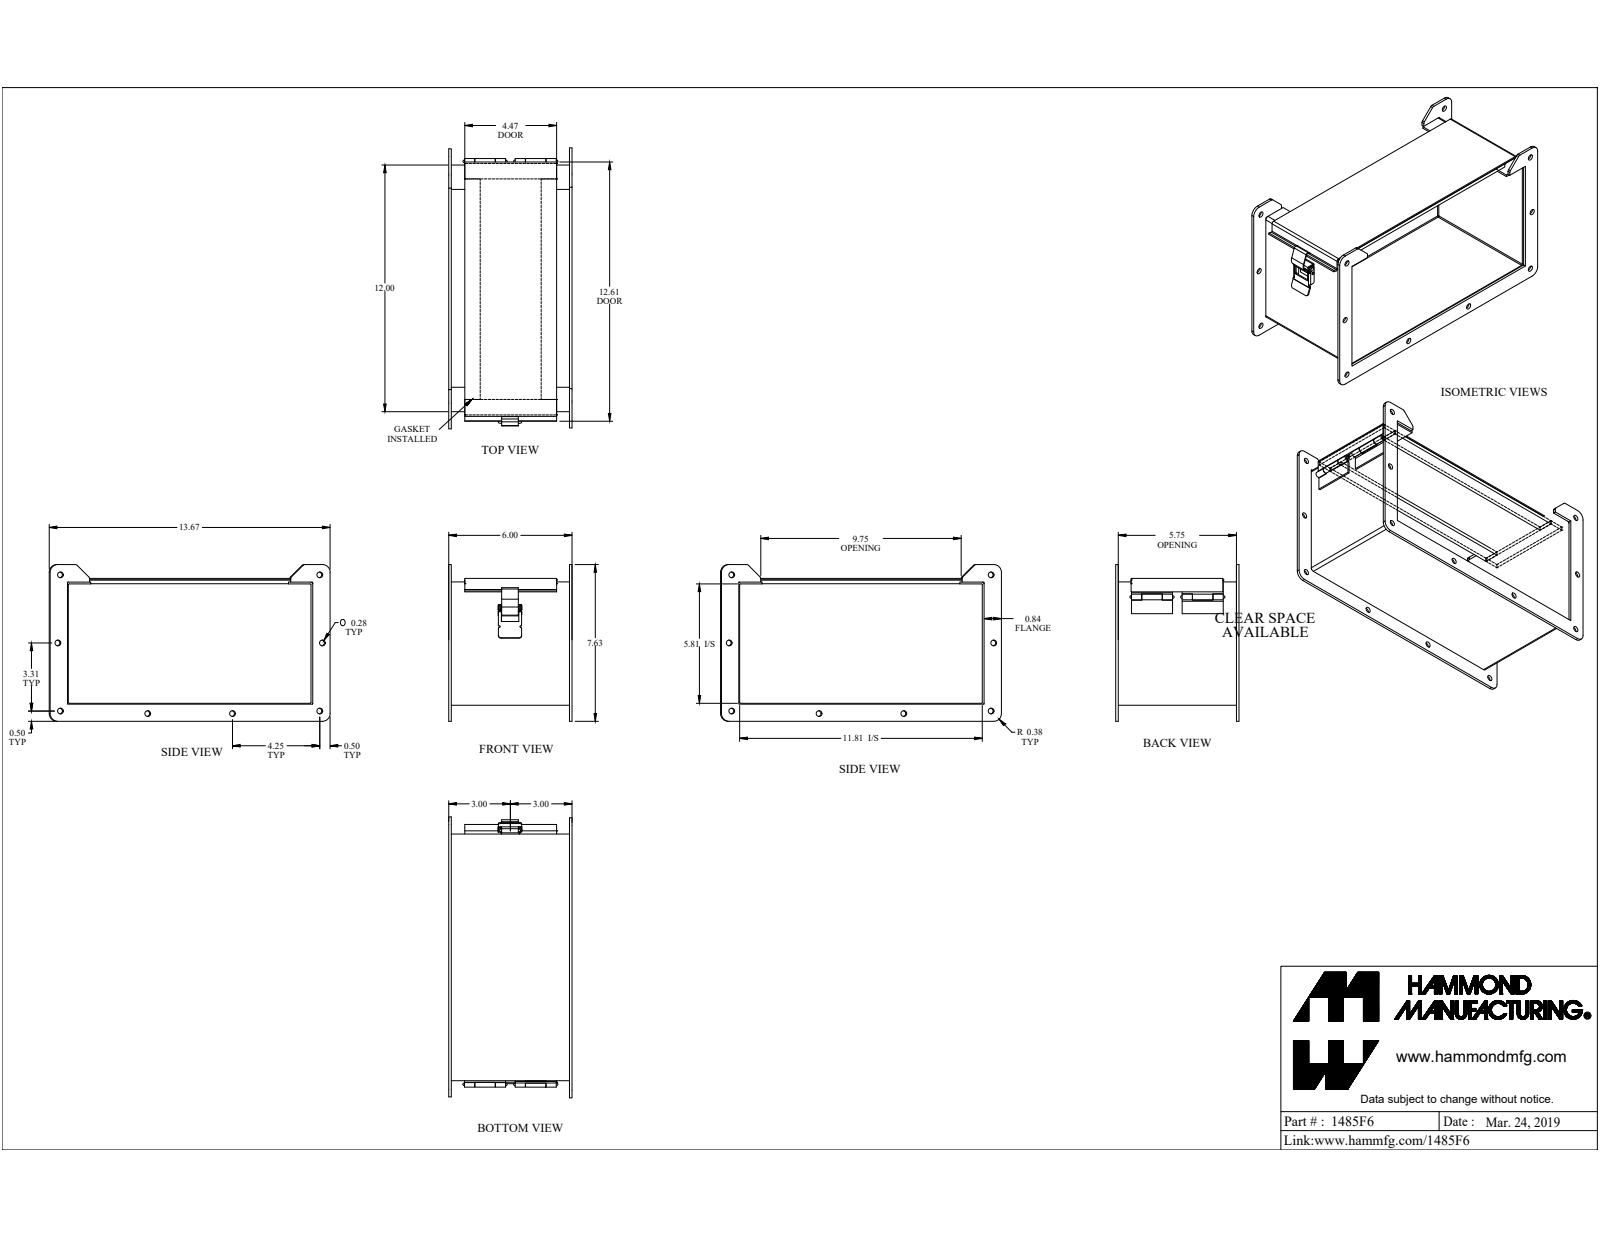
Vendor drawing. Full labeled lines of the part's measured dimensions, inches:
Part name (STEP PRODUCT): 1485F6
STEP written by: SolidWorks 2019 (CONFIG_CONTROL_DESIGN)
Units: inches
Bodies: 17 solids, 304 faces (188 planar, 112 cylindrical, 4 other)
Overall size (bounding box): 13.67 × 7.625 × 6
Volume: 29.58 in³ · Surface area: 627 in²
Round holes (diameter × count): ⌀0.281 ×16, ⌀0.125 ×1, ⌀0.13 ×1, ⌀0.164 ×1
Round bosses / shafts (diameter × count): ⌀0.187 ×2, ⌀0.275 ×1, ⌀0.156 ×1, ⌀0.125 ×1, ⌀0.125 ×1
Partial cylindrical surfaces — rounded edges, fillets, slot ends (radius × count): R0.125 ×11, R0.375 ×8, R0.016 ×7, R0.048 ×4, R0.143 ×4, R0.035 ×3, R0.036 ×3, R0.039 ×3
Main face-to-face distances: 0.095, 6.1, 6.005, 11.905, 0.072, 6.172, 6.077, 6, 12, 11.81
Hole centre spacings: 0.045, 3.315, 6.625, 13.173, 3.313, 3.317, 4.252, 5.564
